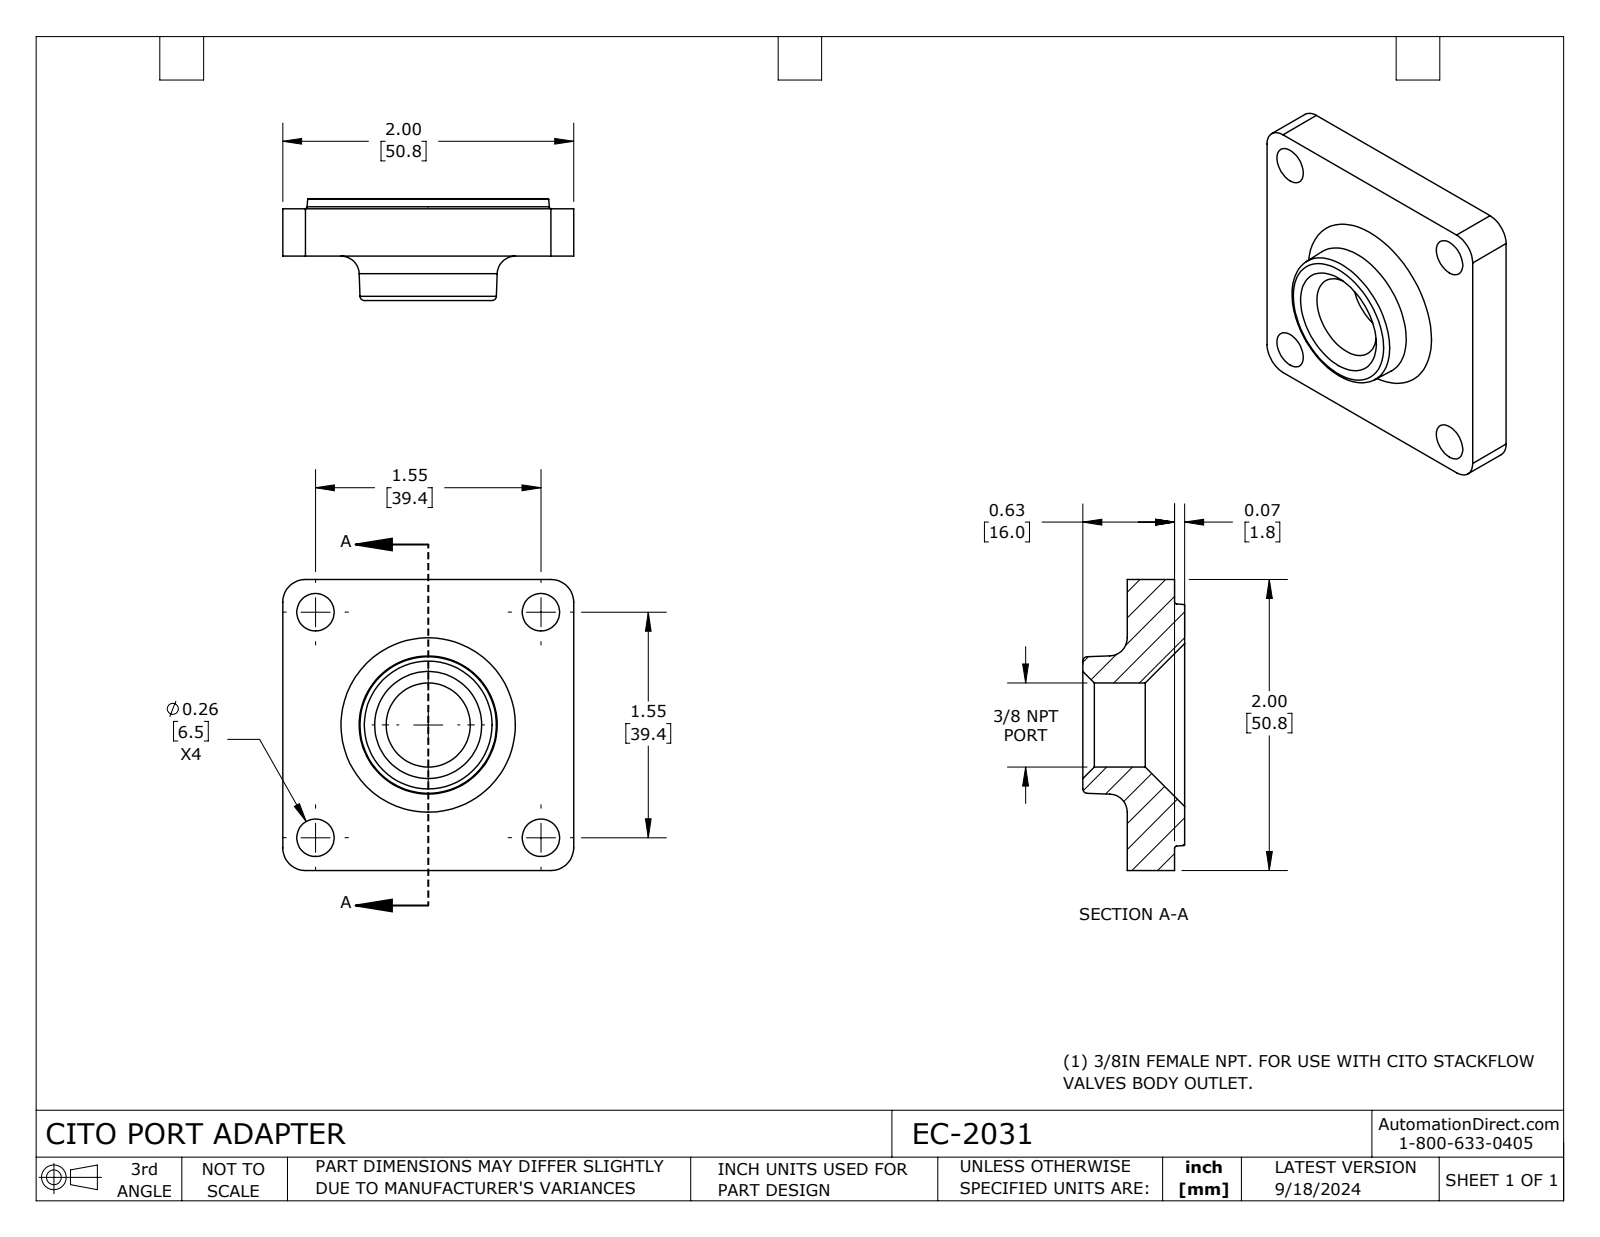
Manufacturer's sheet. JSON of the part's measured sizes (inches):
{"part_name": "EC-2031", "step_written_by": "SolidWorks 2023 (CONFIG_CONTROL_DESIGN)", "units": "inches", "bodies": {"solids": 1, "faces": 38, "planar": 8, "cylindrical": 14, "other": 16}, "overall_size": [2, 2, 0.7], "volume_in3": 1.324, "surface_area_in2": 12.58, "round_holes": [[0.257, 4], [0.578, 1]], "partial_cylinders_radius": [[0.156, 4]], "face_to_face_distances": [0.325, 0.395, 0.07, 2, 0.305, 0.63, 0.7], "hole_center_spacings": [1.096, 1.55, 2.191]}
